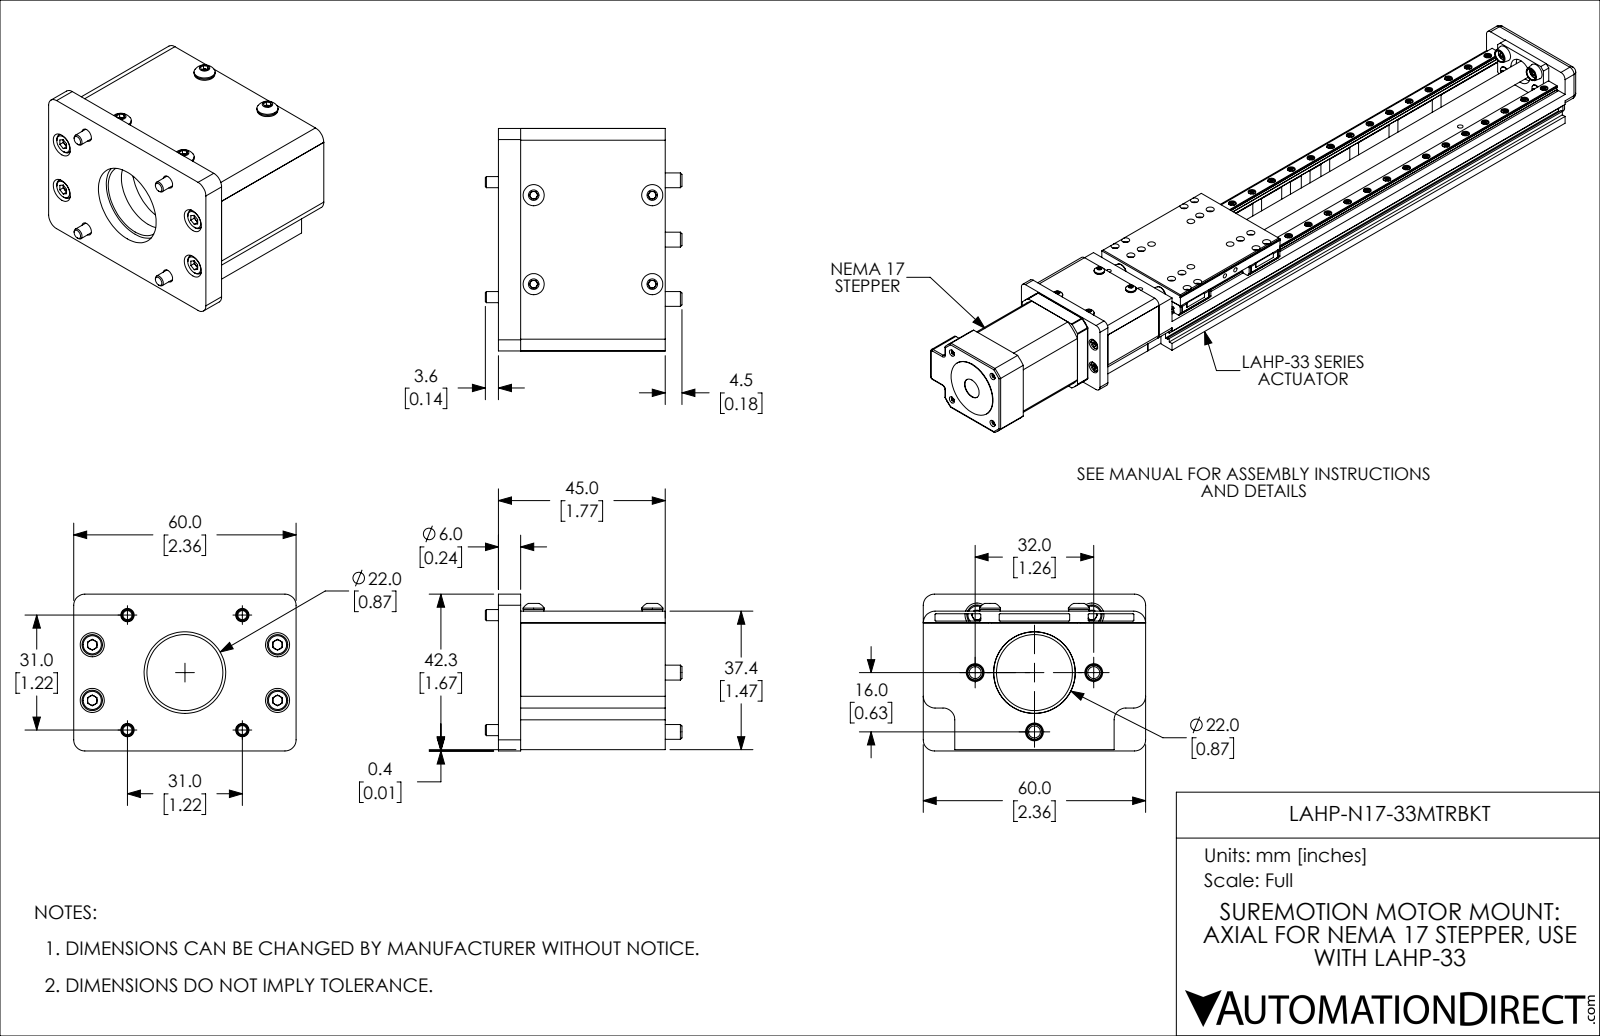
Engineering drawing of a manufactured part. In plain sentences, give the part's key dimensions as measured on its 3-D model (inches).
The part is named "LAHP-N17-33MTRBKT". Its 3-D file was written by "SolidWorks 2019 (CONFIG_CONTROL_DESIGN)". It is 33 solids with 691 faces: 319 planar, 240 cylindrical and 132 other. Overall it measures 2.362 by 2.089 by 1.665 inches. Its volume is 3.455 cubic inches and its surface area 53.76 square inches. Round holes: 12 of diameter 0.098, 12 of diameter 0.126, 12 of diameter 0.142, 8 of diameter 0.256, 3 of diameter 0.169, 3 of diameter 0.189, 3 of diameter 0.315, 1 of diameter 0.807, 1 of diameter 0.867, 1 of diameter 0.867. Round bosses or shafts: 12 of diameter 0.217, 12 of diameter 0.118, 4 of diameter 0.224, 3 of diameter 0.276, 3 of diameter 0.157, 1 of diameter 0.866. Partial cylindrical surfaces (rounded edges, fillets, slot ends): 12 of radius 0.01, 10 of radius 0.125, 4 of radius 0.118. The main face-to-face distances are 0.079, 0.125, 0.236, 0.02, 0.098, 1.346, 1.471, 1.366, 0.105, 1.444. The hole center spacings are 0.611, 1.382, 0.217, 0.396, 0.406, 0.461, 0.489, 0.71.
